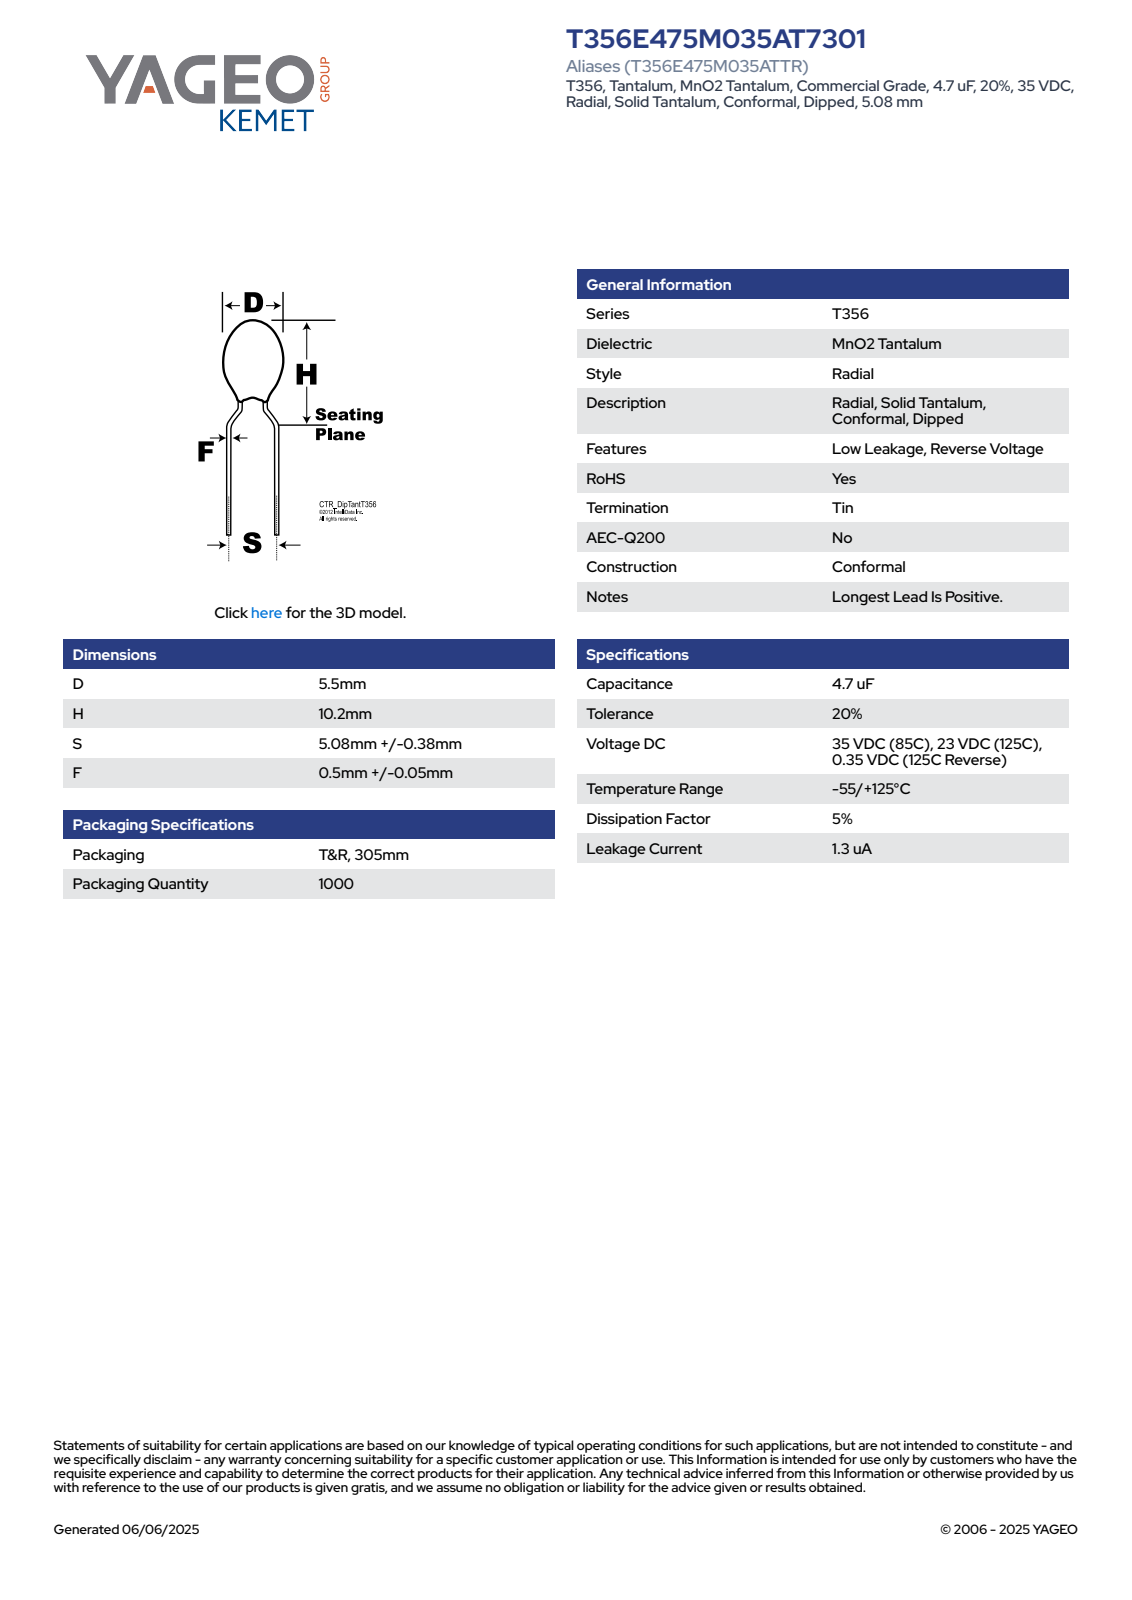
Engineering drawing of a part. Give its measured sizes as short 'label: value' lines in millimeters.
name: CTR_T356_D5.5H10.2S5.08LL5.56F0.55
written by: SolidWorks 2014 (AUTOMOTIVE_DESIGN)
unit: mm
bodies: 1 solid, 100 faces (27 planar, 18 cylindrical, 55 other)
size: 15.76 × 5.63 × 5.5
volume: 156 mm³; area: 178 mm²
bosses: 6× ⌀0.55, 1× ⌀5.5
rounds: 1× R2.74
face distances: 7.12, 8.64, 15.76, 13.32, 4.68, 2.44, 12.42, 3.78, 0.9, 3.34
